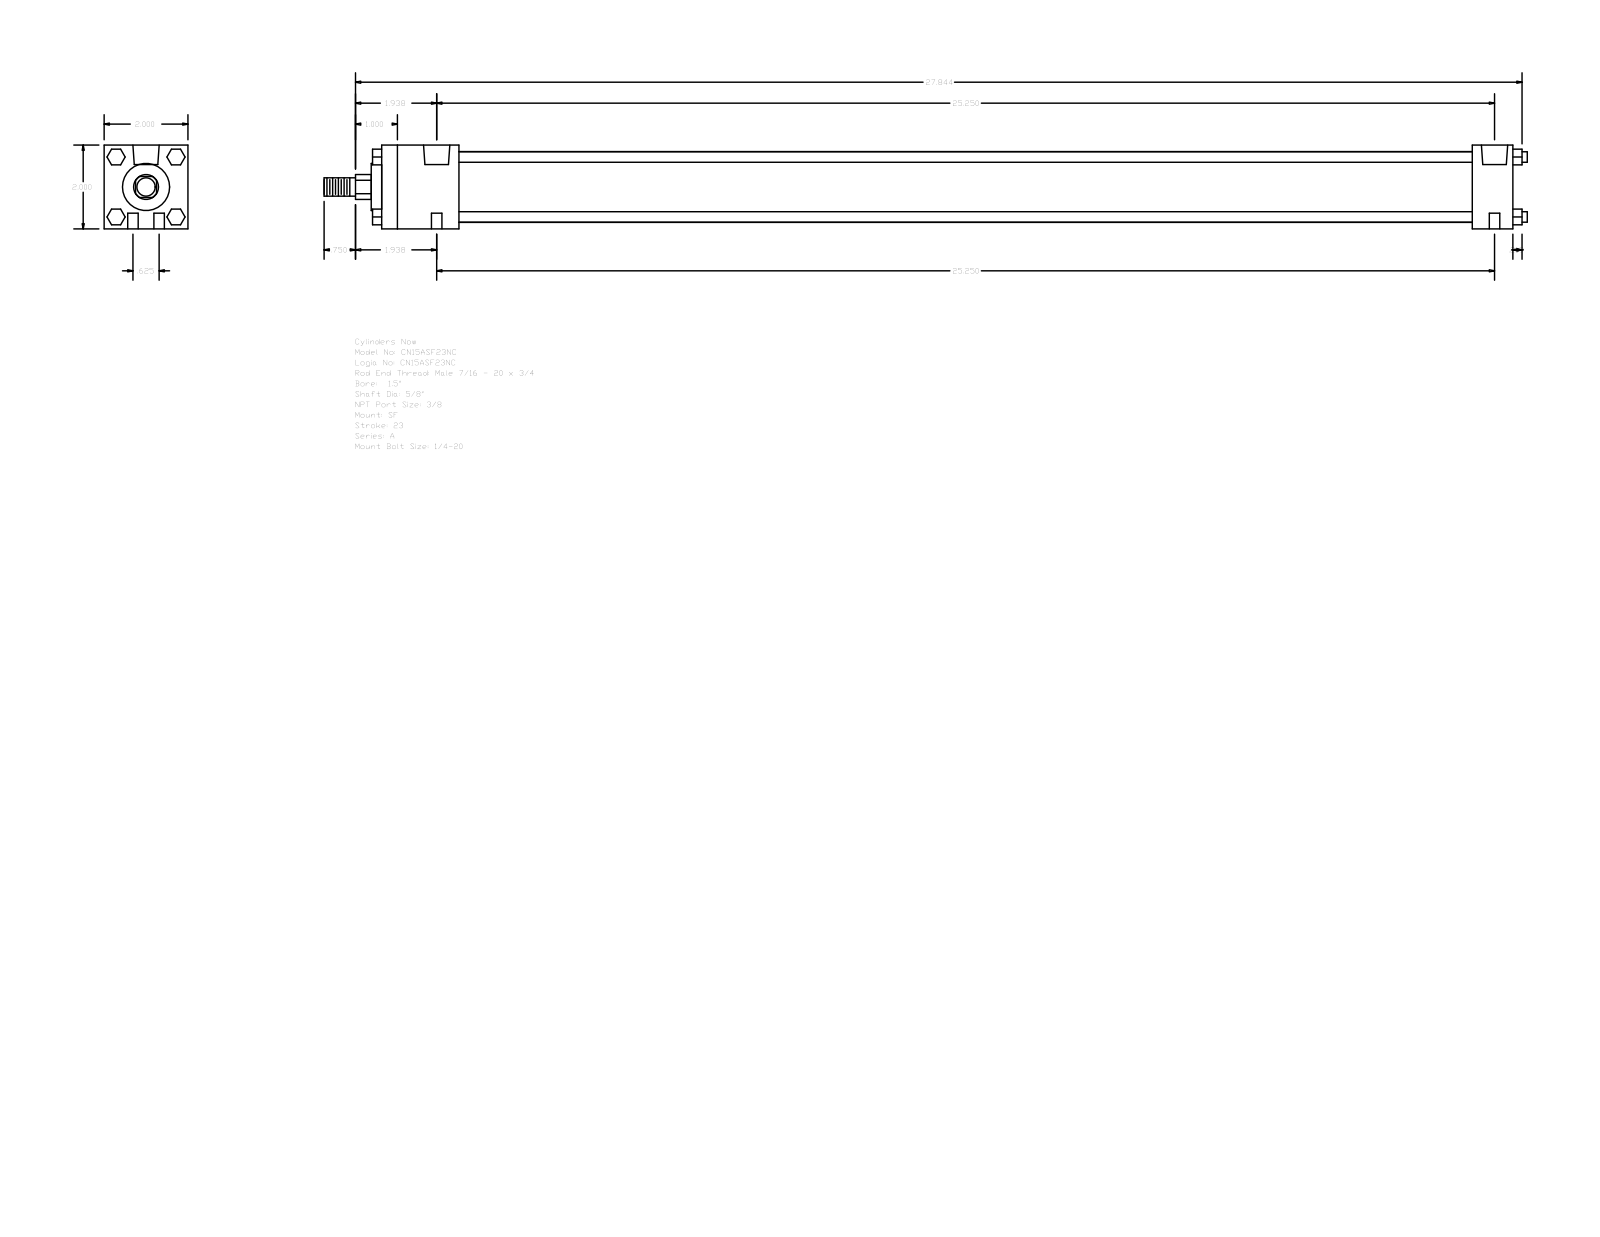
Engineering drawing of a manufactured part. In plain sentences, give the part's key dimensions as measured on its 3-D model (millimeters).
The part is named "A_SF__0150_0.625". Its 3-D file was written by "GSSL Pune (CONFIG_CONTROL_DESIGN)". It is 0 solids with 124 faces: 94 planar, 30 cylindrical and 0 other. Overall it measures 729.46 by 50.8 by 50.8 millimeters. Round holes: 4 of diameter 6.35, 2 of diameter 5.56, 2 of diameter 15.93. Round bosses or shafts: 4 of diameter 6.35, 1 of diameter 42.93, 1 of diameter 28.57, 1 of diameter 15.88, 1 of diameter 11.11. Partial cylindrical surfaces (rounded edges, fillets, slot ends): 1 of radius 7.54. The main face-to-face distances are 50.8, 685.79, 46.83, 661.19, 614.36, 638.96, 24.6, 6.35, 9.52, 53.18. The hole center spacings are 7.94, 641.4, 641.35, 15.88, 641.55, 633.41.
